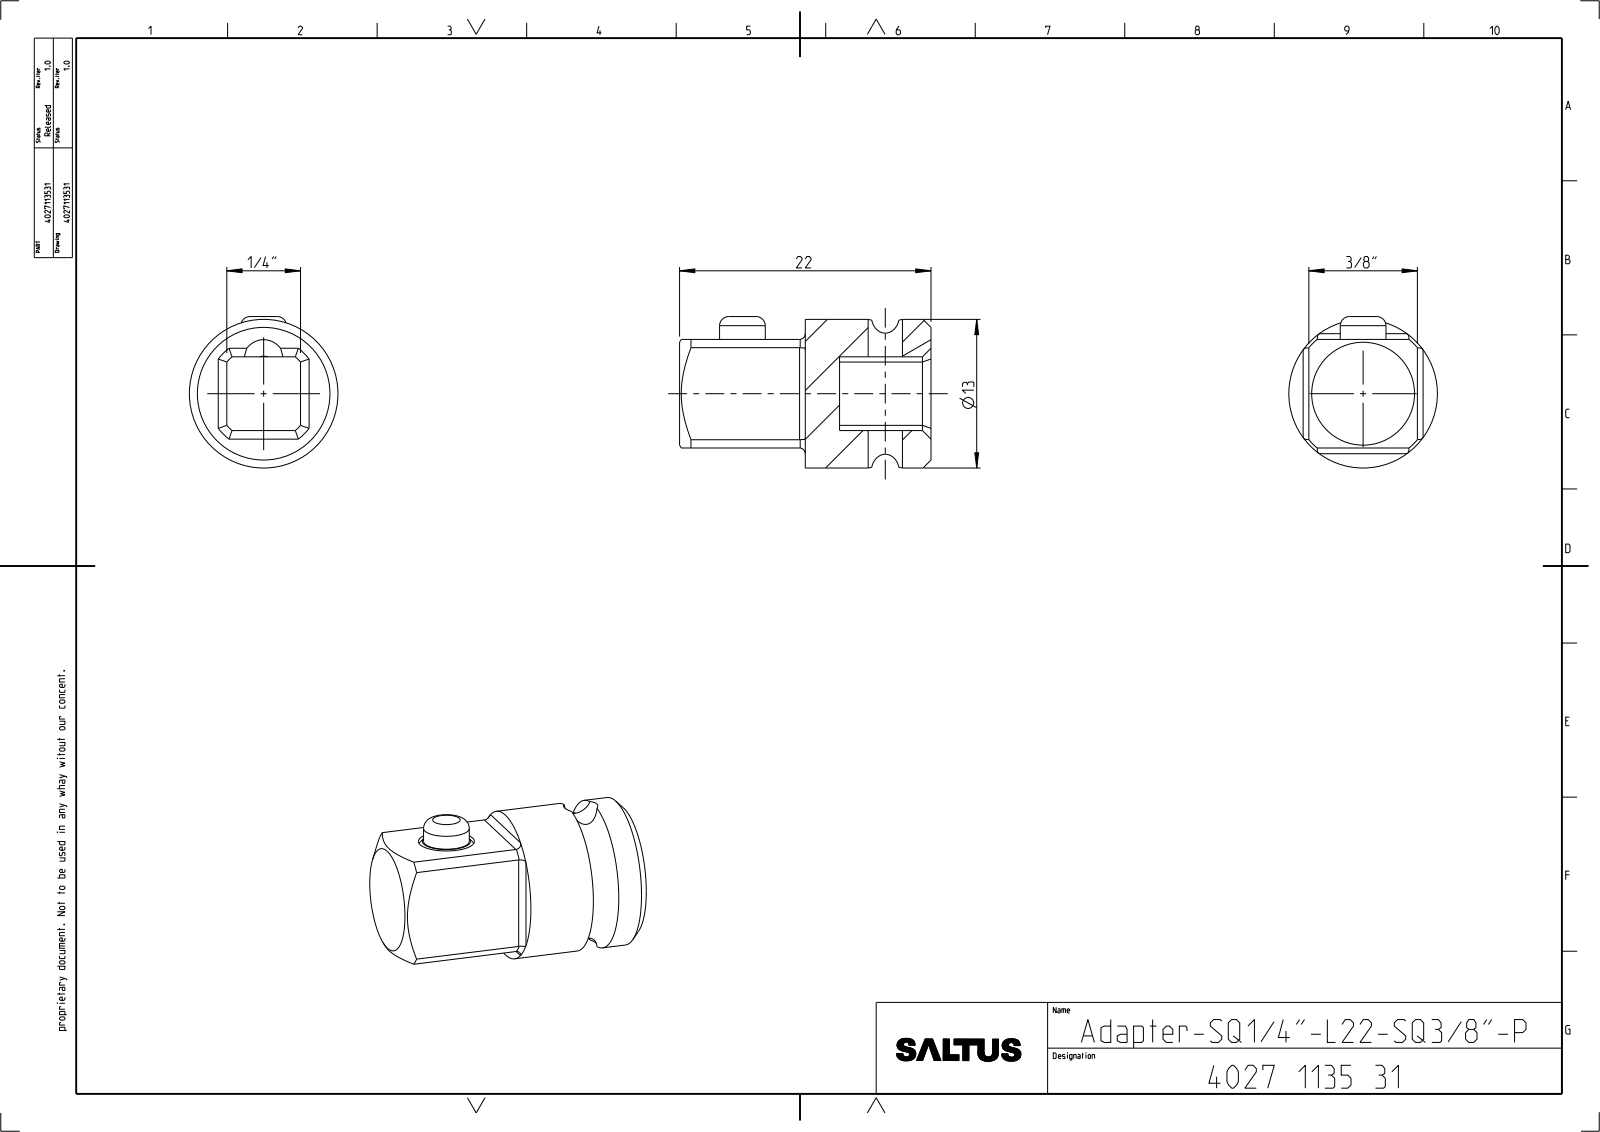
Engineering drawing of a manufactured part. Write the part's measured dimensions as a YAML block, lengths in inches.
part_name: "4027113531"
step_written_by: "CREO PARAMETRIC BY PTC INC, 2022414 (CONFIG_CONTROL_DESIGN)"
units: inches
bodies: {solids: 1, faces: 70, planar: 23, cylindrical: 27, other: 20}
overall_size: [0.866, 0.522, 0.512]
volume: 0.113
surface_area: 2.348
round_holes:
  - {diameter: 0.118, count: 1}
  - {diameter: 0.193, count: 1}
round_bosses_or_shafts:
  - {diameter: 0.512, count: 1}
  - {diameter: 0.189, count: 1}
  - {diameter: 0.157, count: 1}
partial_cylinders:
  - {radius: 0.02, count: 4}
  - {radius: 0.079, count: 1}
  - {radius: 0.167, count: 1}
  - {radius: 0.245, count: 1}
face_to_face_distances: [0.374, 0.06, 0.314, 0.254, 0.433, 0.866, 0.315, 0.551, 0.118, 0.246]
hole_center_spacings: [0.492]
